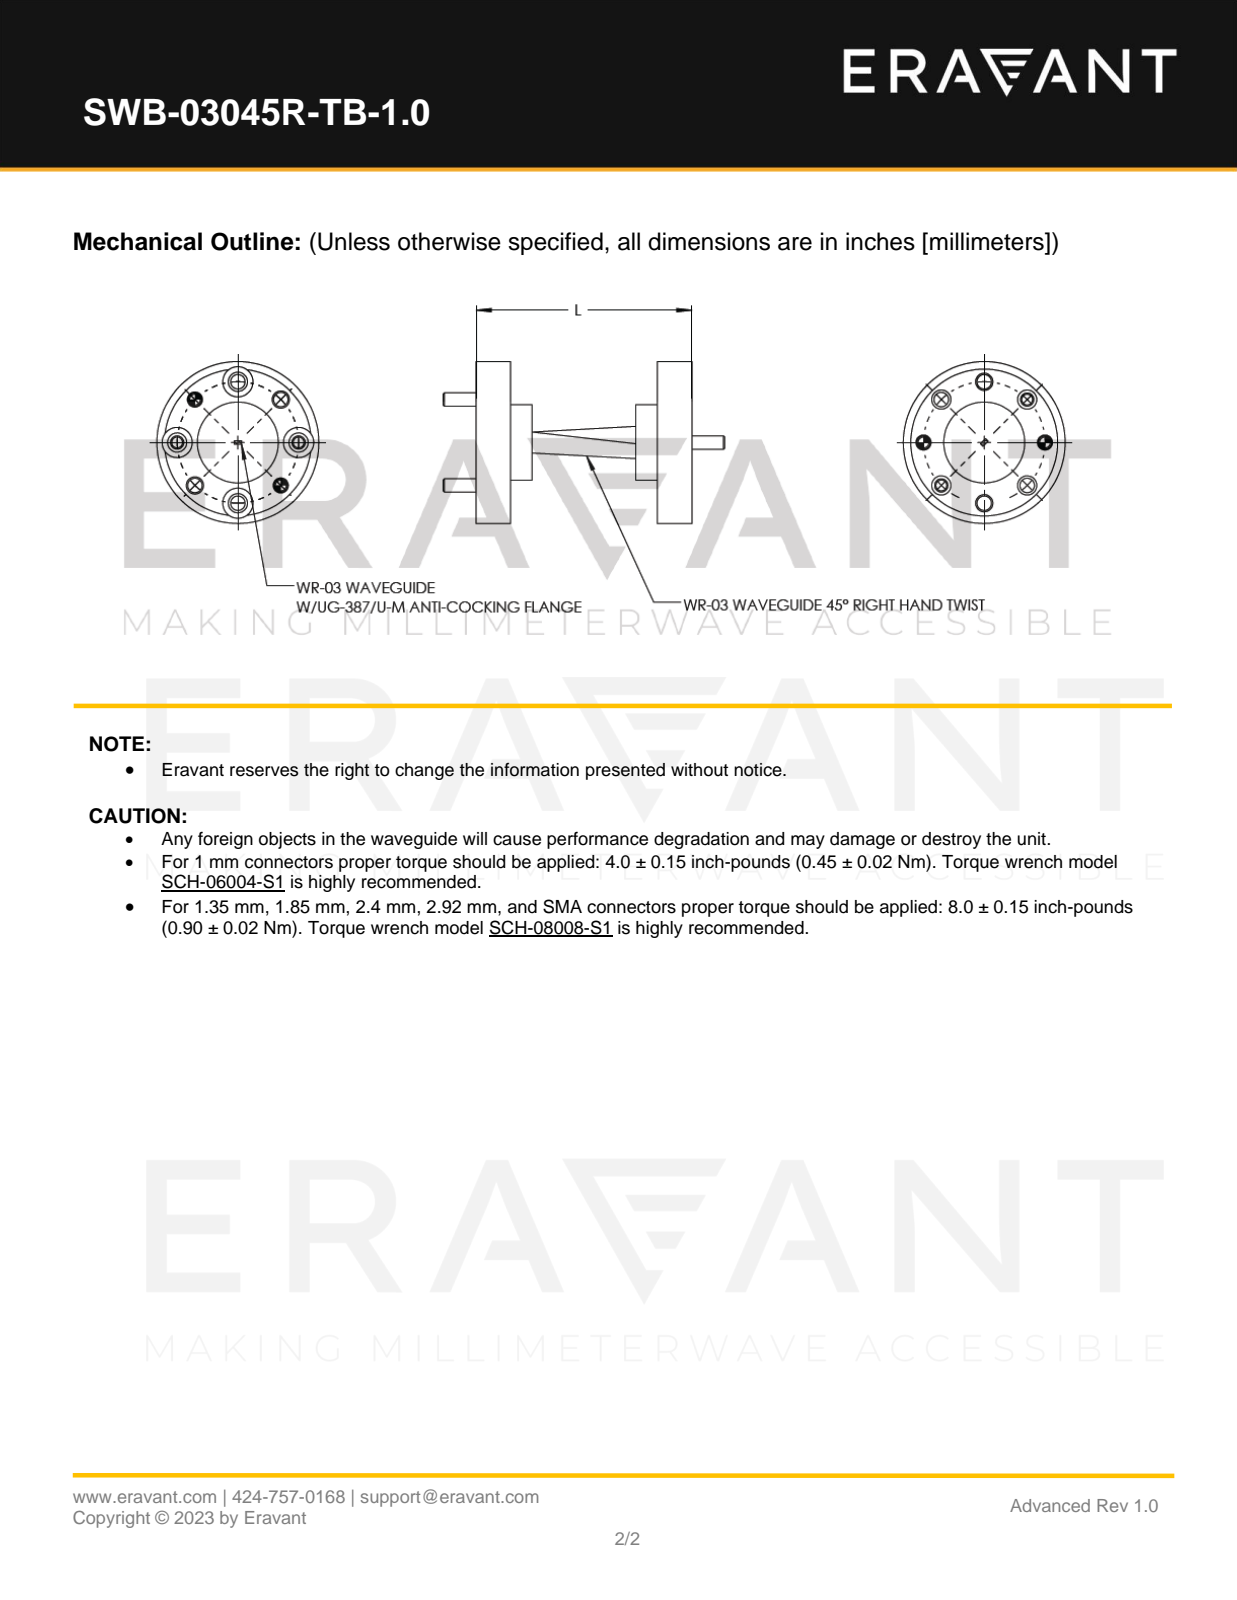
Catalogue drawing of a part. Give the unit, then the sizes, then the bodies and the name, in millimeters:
Units: millimetres
Overall size (bounding box): 33.1 × 19.1 × 19.1
Round holes (diameter × count): ⌀2.3 ×8, ⌀3.6 ×8, ⌀1.5 ×4, ⌀1.7 ×4, ⌀17.3 ×1
Round bosses / shafts (diameter × count): ⌀1.6 ×4, ⌀19.1 ×1, ⌀9.5 ×1, ⌀8.9 ×1
Main face-to-face distances: 4.1, 21.3, 0.5, 24.9, 3.6, 20.8, 17.3, 2.5, 25.4, 24.4
Hole centre spacings: 5.5, 10.1, 7.1, 13.2, 13.2, 7.1, 14.3, 14.3
Volume: 2 360 mm³ · Surface area: 2 486 mm²
Bodies: 5 solids, 151 faces (34 planar, 77 cylindrical, 40 other)
Part name (STEP PRODUCT): WB-T03-5R-A-L, Defeatured
STEP written by: SolidWorks 2021 (AUTOMOTIVE_DESIGN)
